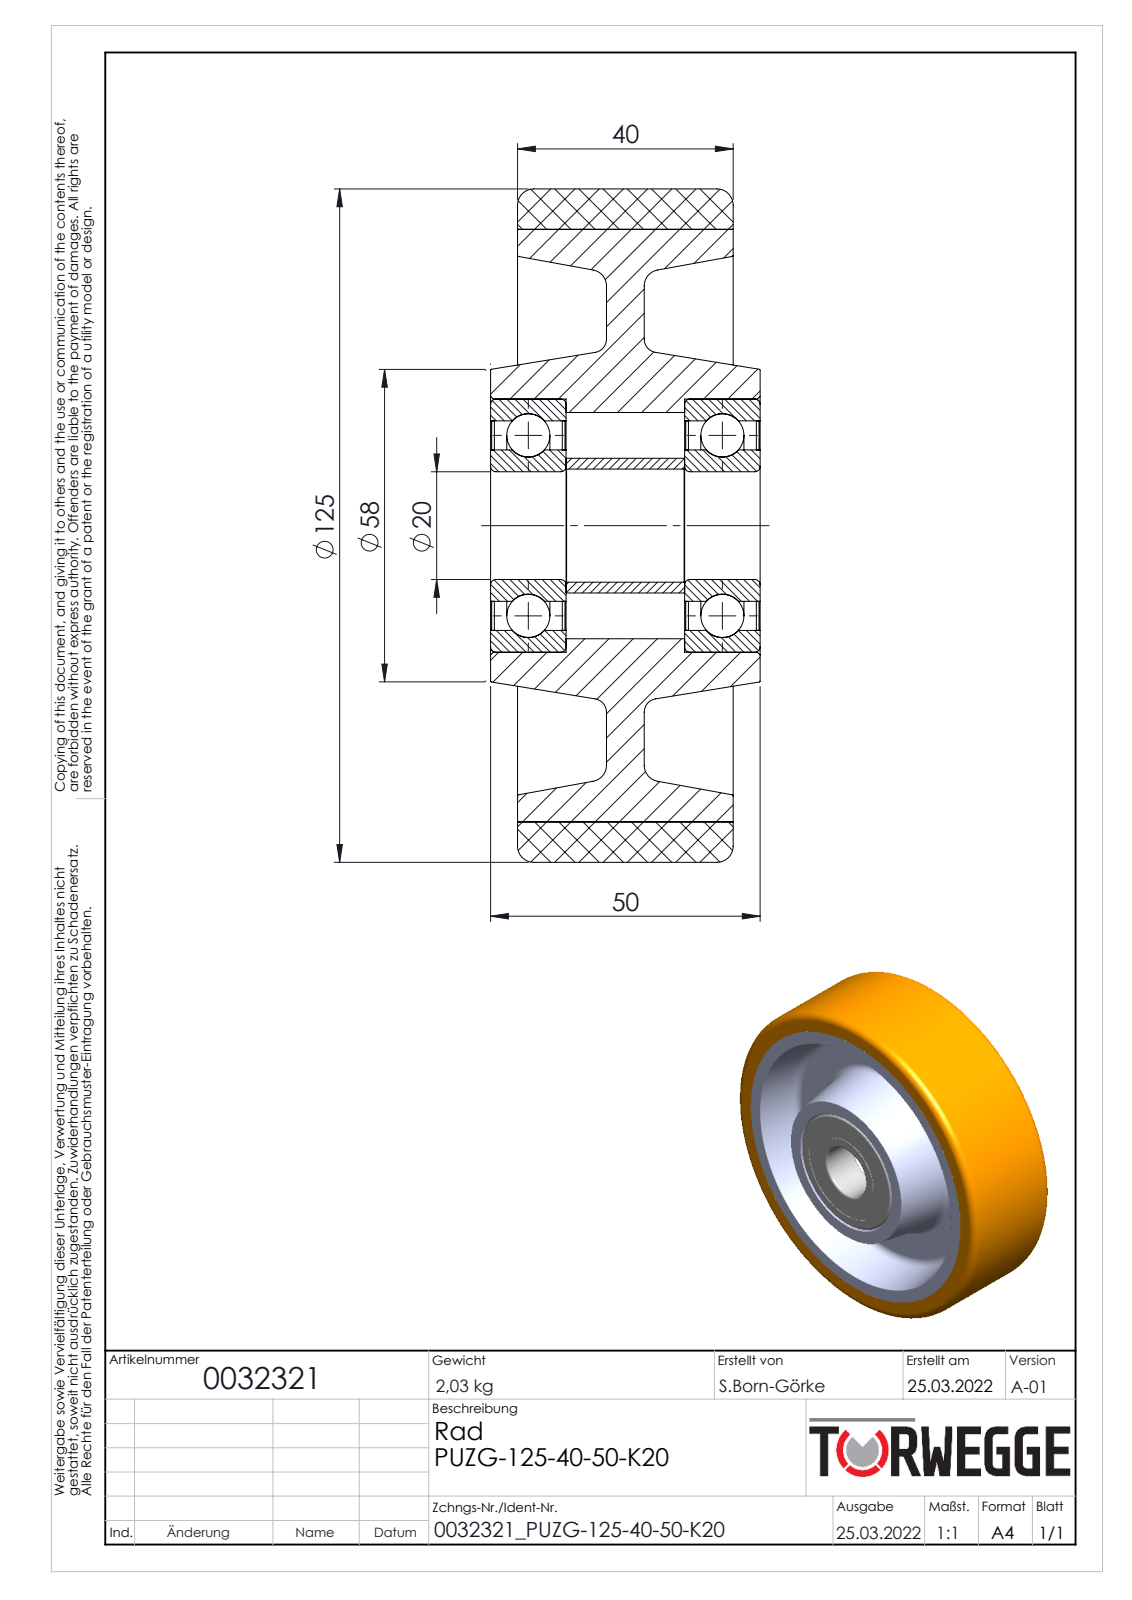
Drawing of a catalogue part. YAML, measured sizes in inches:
part_name: "0032321"
step_written_by: "SolidWorks 2020 (AUTOMOTIVE_DESIGN)"
units: inches
bodies: {solids: 13, faces: 160, planar: 28, cylindrical: 56, other: 76}
overall_size: [4.921, 4.921, 1.969]
volume: 20.23
surface_area: 177.5
round_holes:
  - {diameter: 0.787, count: 1}
  - {diameter: 0.827, count: 1}
  - {diameter: 1.106, count: 1}
  - {diameter: 1.531, count: 1}
  - {diameter: 1.654, count: 1}
  - {diameter: 1.85, count: 1}
  - {diameter: 4.331, count: 1}
round_bosses_or_shafts:
  - {diameter: 4.921, count: 1}
  - {diameter: 0.984, count: 1}
face_to_face_distances: [0.65, 0.925, 1.417, 1.575, 0.197, 0.846, 1.122, 1.772, 0.276, 0.028]
